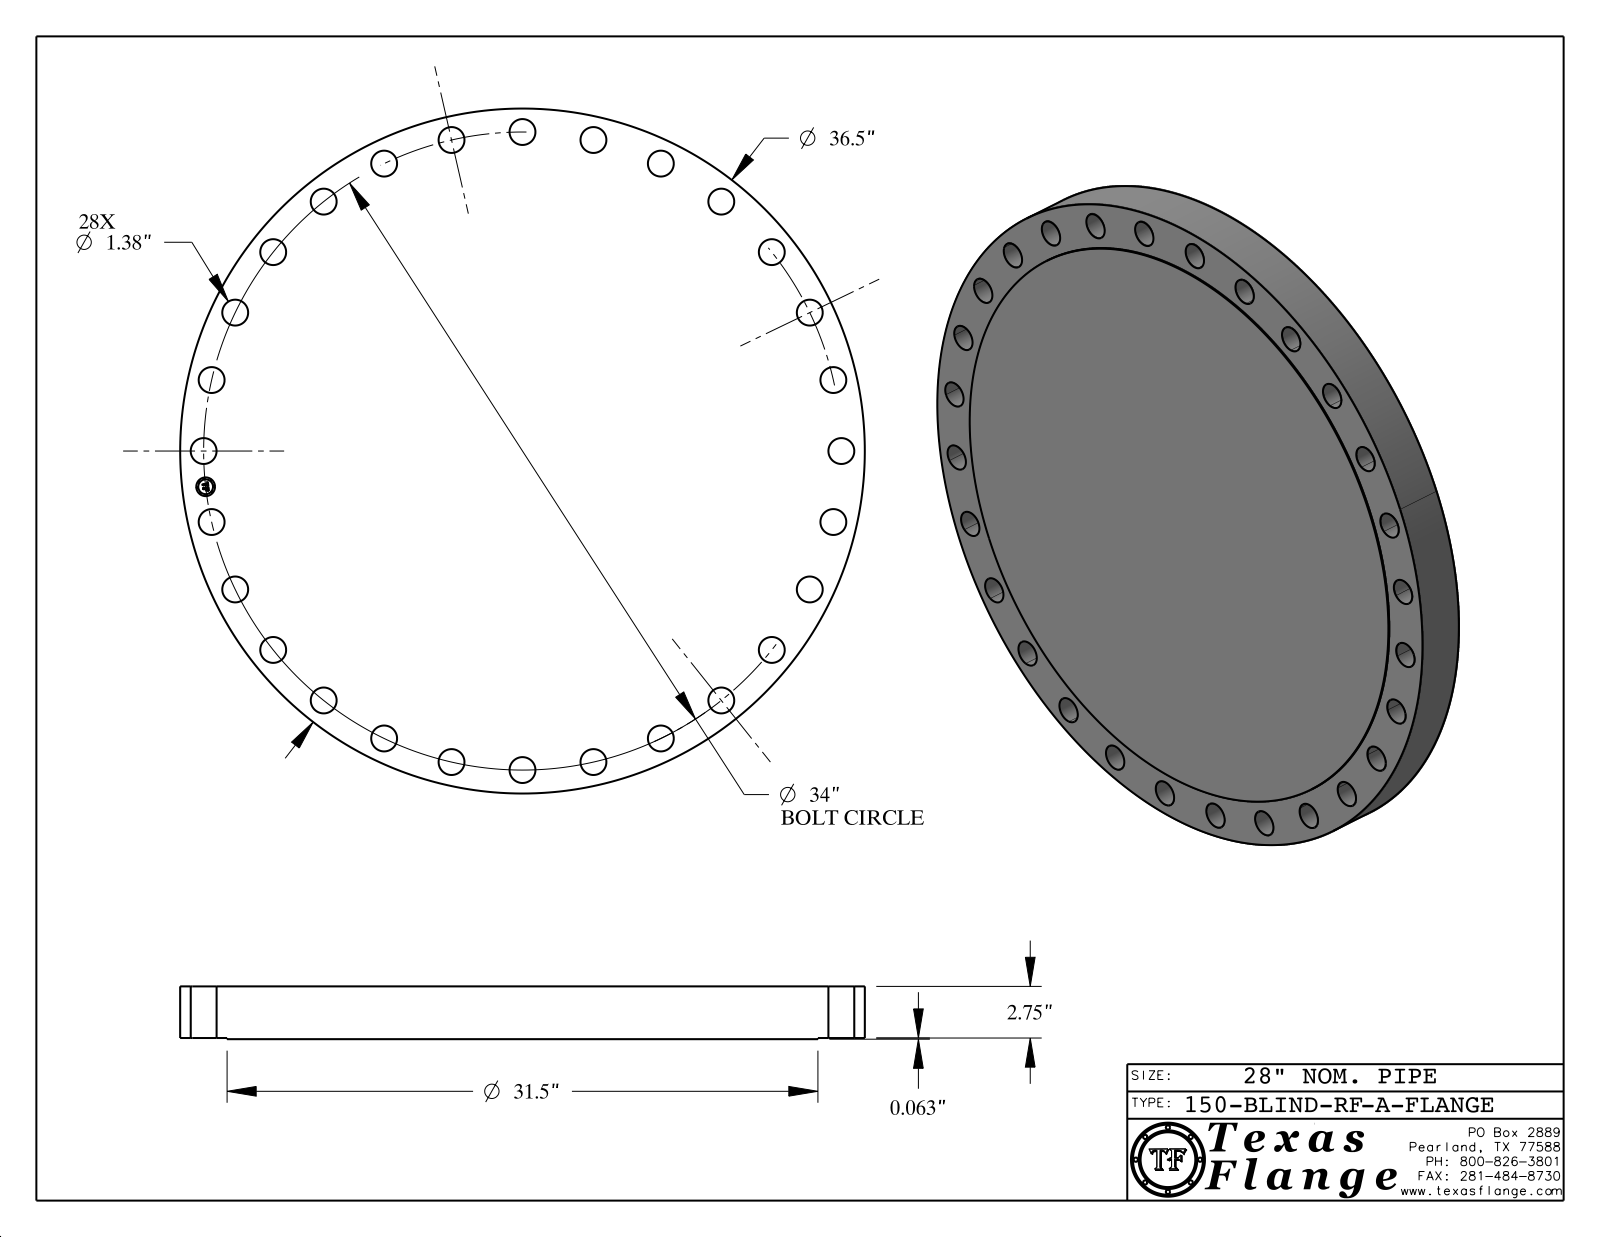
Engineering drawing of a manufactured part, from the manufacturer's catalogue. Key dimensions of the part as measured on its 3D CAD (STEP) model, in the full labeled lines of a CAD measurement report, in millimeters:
Part name (STEP PRODUCT): 150-BLIND-RF, Series A
STEP written by: CATIA V5 STEP AP214 (AUTOMOTIVE_DESIGN)
Units: millimetres
Bodies: 1 solid, 448 faces (368 planar, 80 cylindrical, 0 other)
Overall size (bounding box): 927.1 × 927.1 × 71.5
Volume: 46 060 000 mm³ · Surface area: 1 719 000 mm²
Round holes (diameter × count): ⌀35.1 ×28, ⌀25.4 ×1
Round bosses / shafts (diameter × count): ⌀1.5 ×8, ⌀927.1 ×1, ⌀800.1 ×1, ⌀20 ×1
Main face-to-face distances: 71.5, 1.6, 69.9, 0.4, 71.1, 69.5, 7.6, 7.4, 1.4, 4.9
Hole centre spacings: 96.7, 192.2, 778.1, 858.2, 285.2, 459.5, 538.4, 841.9
